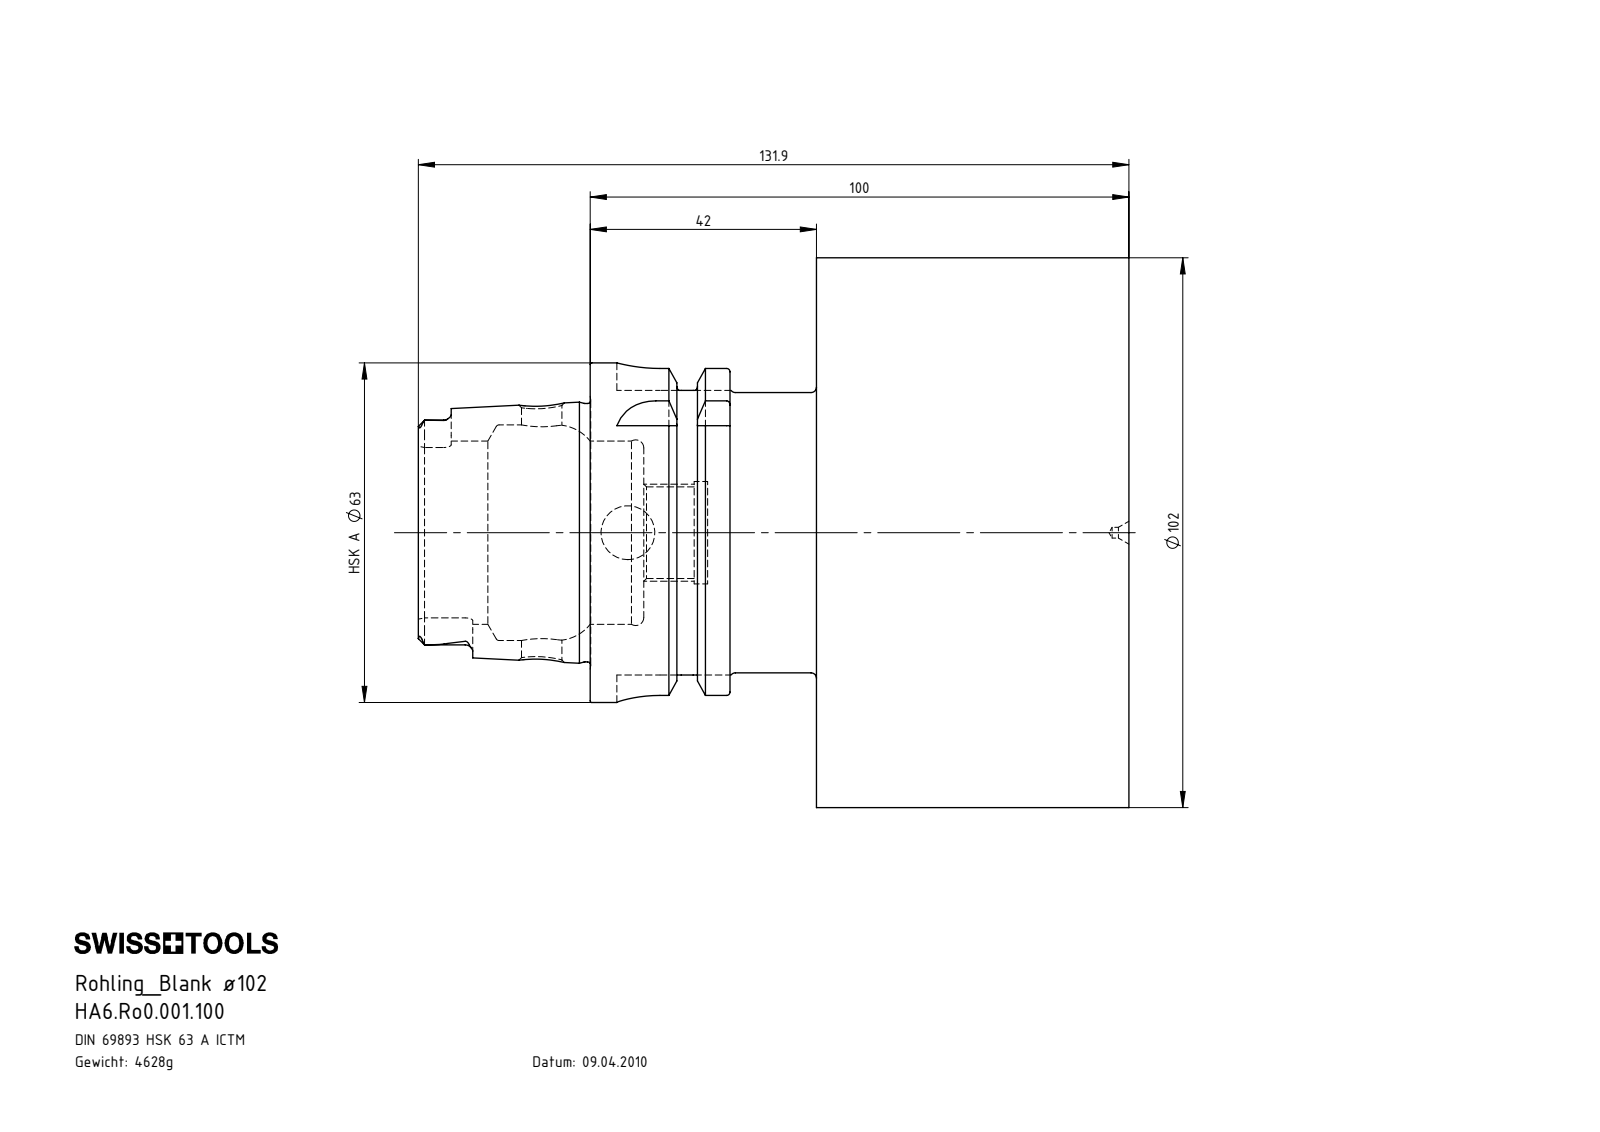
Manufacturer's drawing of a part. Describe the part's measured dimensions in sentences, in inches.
The part is named "HA6.Ro0.001.100". Its 3-D file was written by "SolidWorks 2017 (AUTOMOTIVE_DESIGN)". It is 1 solid with 123 faces: 48 planar, 32 cylindrical and 43 other. Overall it measures 5.193 by 4.016 by 4.016 inches. Its volume is 35.98 cubic inches and its surface area 85.87 square inches. Round holes: 1 of diameter 0.079, 1 of diameter 0.295, 1 of diameter 0.394, 1 of diameter 0.669, 1 of diameter 0.748, 1 of diameter 1.339, 1 of diameter 1.575. Round bosses or shafts: 1 of diameter 4.016, 1 of diameter 2.48, 1 of diameter 2.163, 1 of diameter 2.047, 1 of diameter 1.887. Partial cylindrical surfaces (rounded edges, fillets, slot ends): 6 of radius 0.055, 4 of radius 0.315, 2 of radius 0.111, 2 of radius 0.113. The main face-to-face distances are 2.283, 1.654, 3.937, 1.022, 0.632, 2.915, 0.63, 0.392, 1.262, 3.545.
